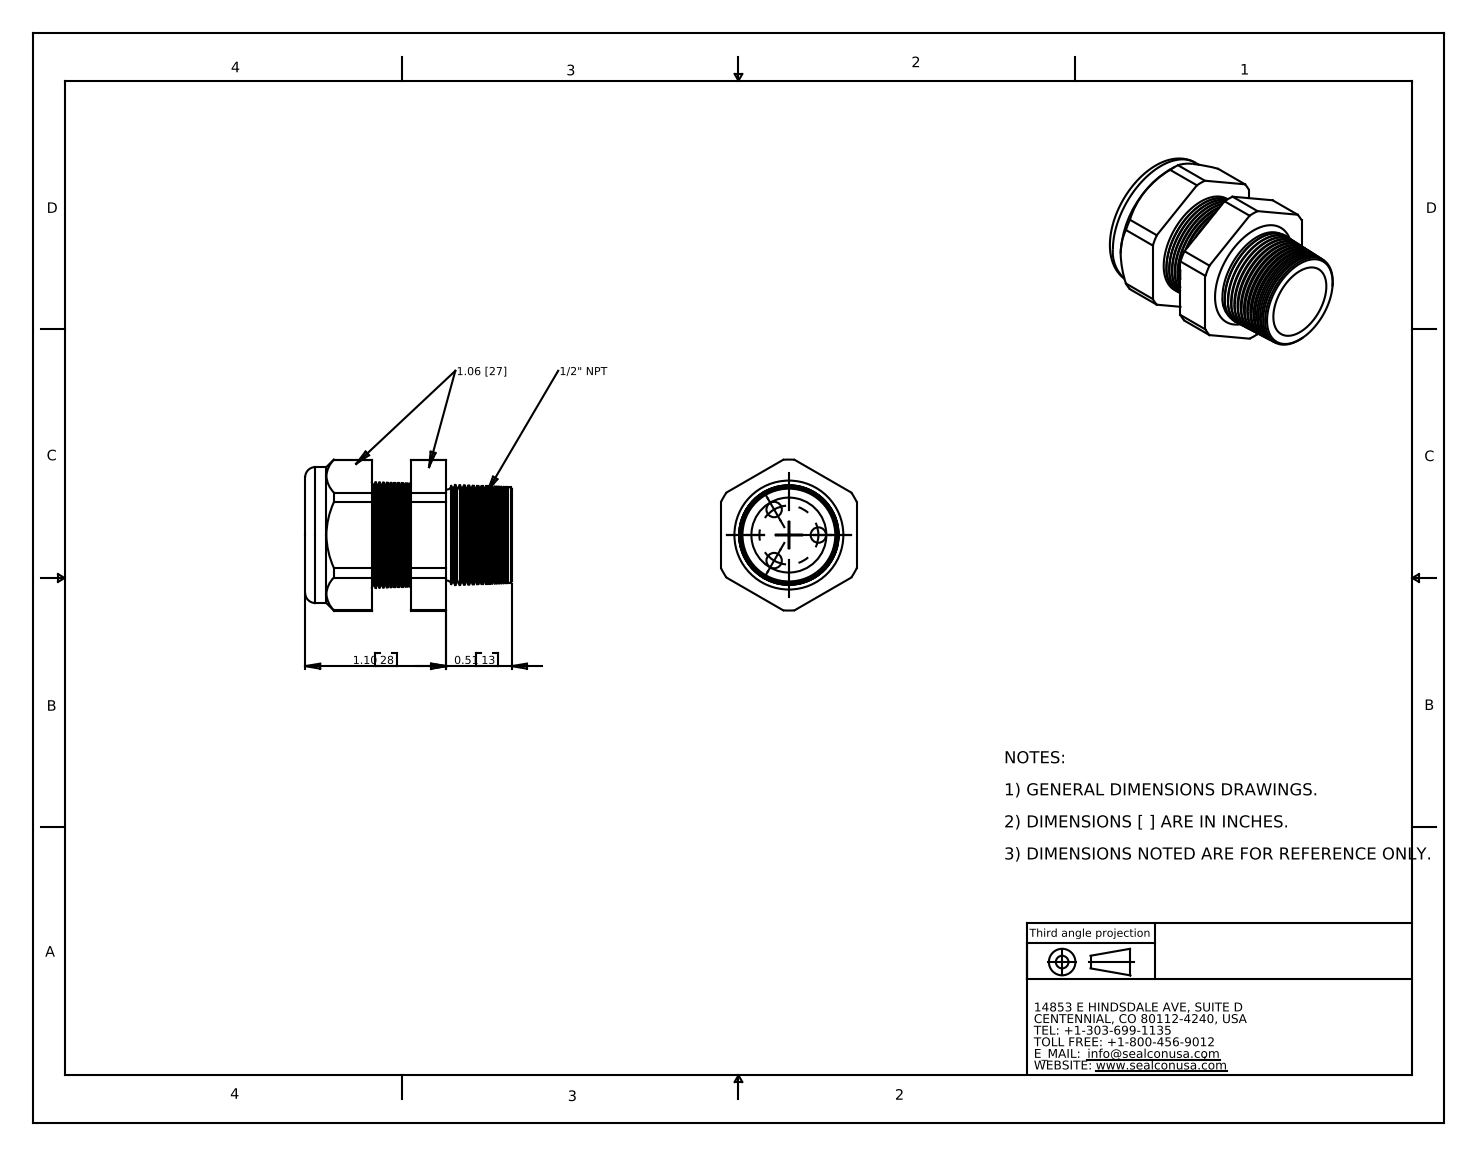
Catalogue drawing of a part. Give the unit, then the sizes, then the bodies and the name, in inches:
Units: inches
Overall size (bounding box): 1.61 × 1.177 × 1.06
Round holes (diameter × count): ⌀0.12 ×3, ⌀0.58 ×1, ⌀0.6 ×1
Round bosses / shafts (diameter × count): ⌀1.06 ×1
Partial cylindrical surfaces — rounded edges, fillets, slot ends (radius × count): R0.588 ×1
Main face-to-face distances: 1.06, 0.305, 0.58, 0.276, 0.52, 0.824, 1.1, 0.35, 0.17, 0.474
Hole centre spacings: 0.23, 0.398, 0.23, 0.398
Volume: 0.752 in³ · Surface area: 12.92 in²
Bodies: 2 solids, 204 faces (20 planar, 26 cylindrical, 158 other)
Part name (STEP PRODUCT): CD16N1-GY
STEP written by: SolidWorks 2007 (CONFIG_CONTROL_DESIGN)
